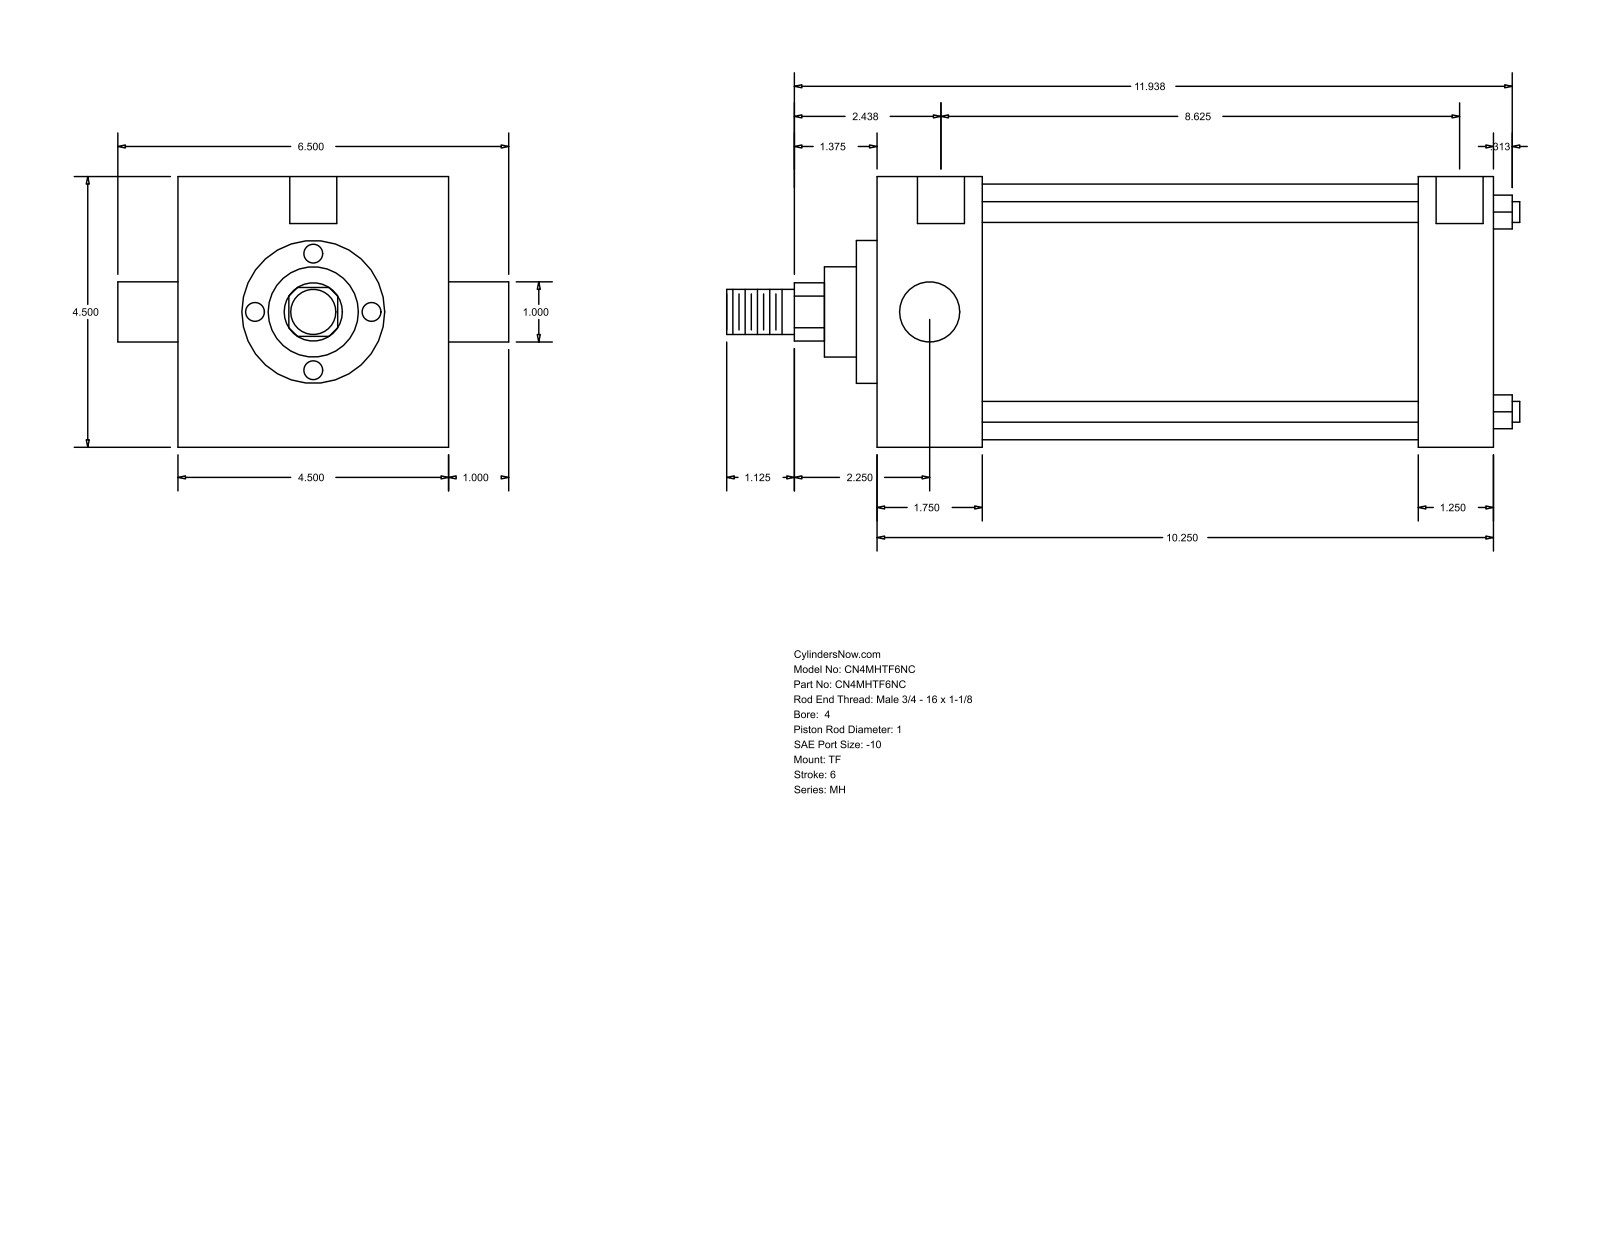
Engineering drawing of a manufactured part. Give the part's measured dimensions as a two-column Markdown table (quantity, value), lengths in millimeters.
| quantity | value |
| --- | --- |
| part name | MH_TF__0400_1 |
| STEP written by | GSSL Pune (CONFIG_CONTROL_DESIGN) |
| units | millimeters |
| bodies | 0 solids, 86 faces (61 planar, 25 cylindrical, 0 other) |
| overall size | 334.96 × 165.1 × 114.3 |
| round holes (diameter × count) | 8.73 × 3, 19.84 × 2 |
| round bosses / shafts (diameter × count) | 8.76 × 4, 25.4 × 2, 107.95 × 1, 60.33 × 1, 38.1 × 1, 19.05 × 1 |
| partial cylindrical surfaces (radius × count) | 12.29 × 1 |
| main face-to-face distances | 114.3, 260.35, 44.46, 215.89, 228.6, 184.14, 31.75, 8.73, 53.19, 237.33 |
| hole center spacings | 1.58, 220.66, 219.08, 222.24 |
